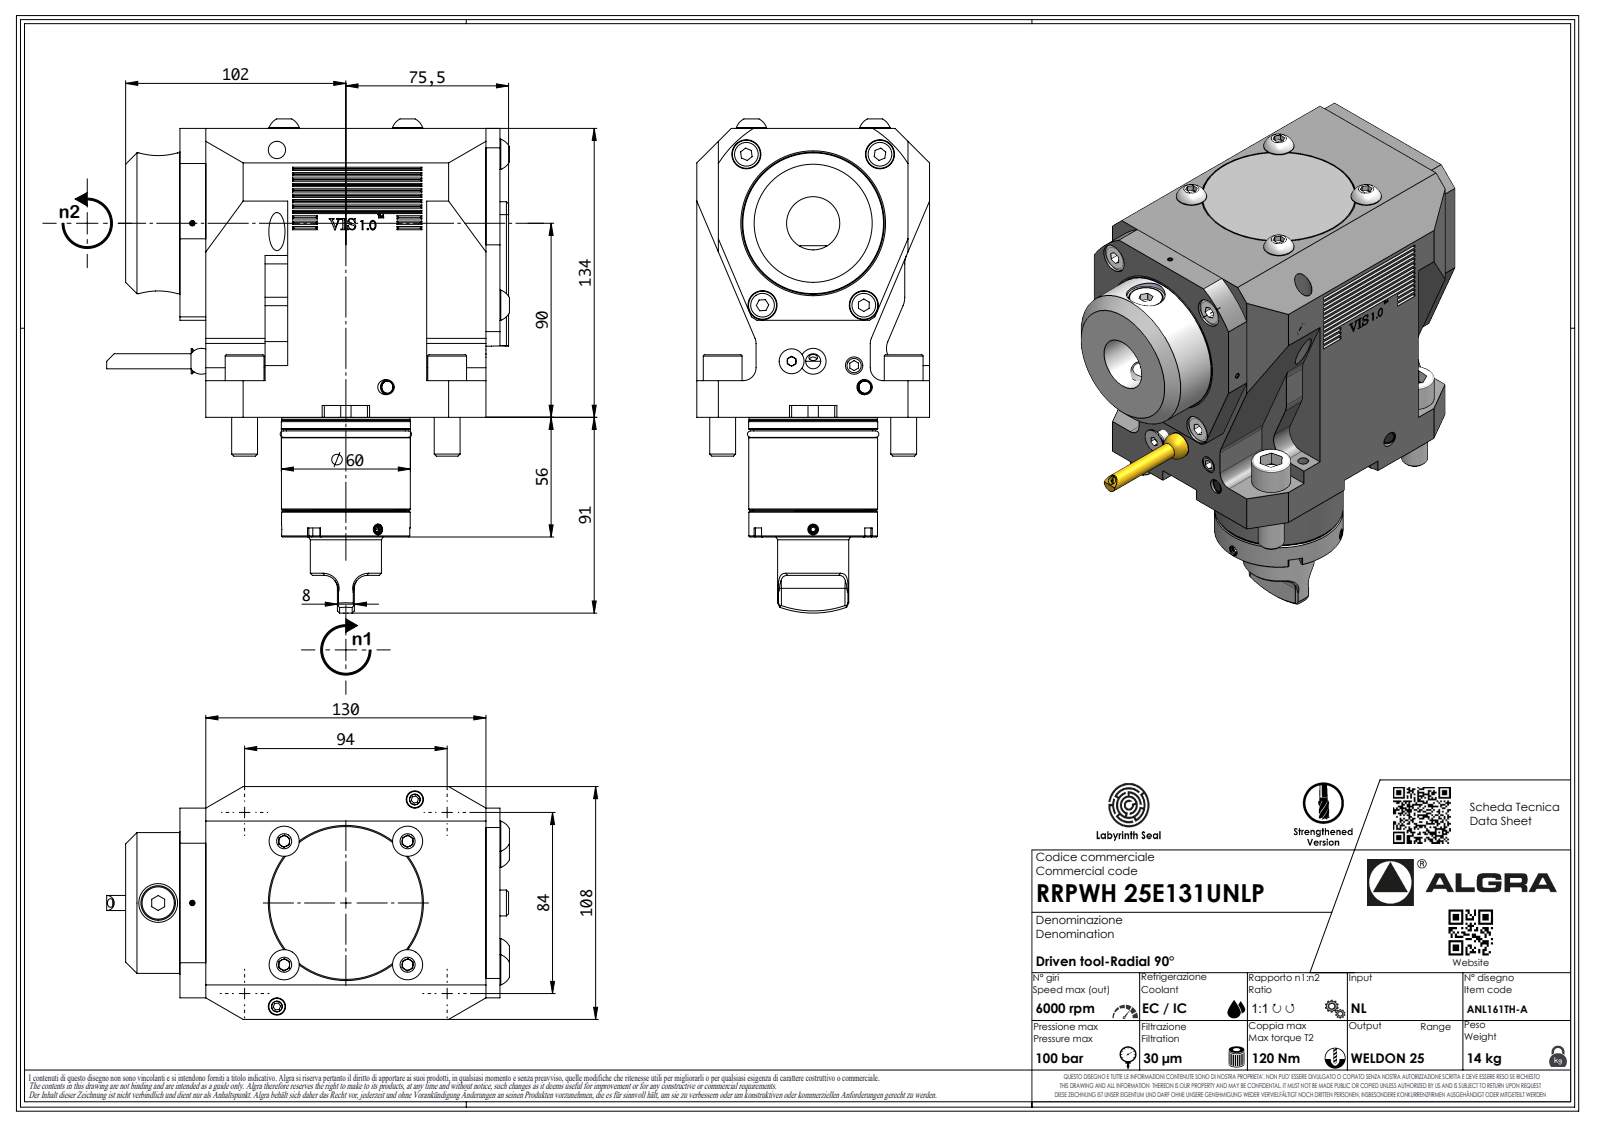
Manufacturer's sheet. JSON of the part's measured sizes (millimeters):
{"part_name": "RRPWH25E131UNLP", "step_written_by": "SolidWorks 2023 (AUTOMOTIVE_DESIGN)", "units": "millimeters", "bodies": {"solids": 1, "faces": 928, "planar": 640, "cylindrical": 111, "other": 177}, "overall_size": [224.8, 177.7, 108], "volume_mm3": 2059000, "surface_area_mm2": 125710, "round_holes": [[2.1, 1]], "round_bosses_or_shafts": [[18, 4], [12, 4], [65.3, 1], [59.9, 1], [59.8, 1], [59.7, 1], [59.5, 1], [55.2, 1]], "partial_cylinders_radius": [[0.2, 21], [8, 18], [6, 11], [0.33, 7], [0.52, 7], [3.7, 7], [10, 4], [3, 3]], "face_to_face_distances": [134, 108, 12, 27.5, 102.5, 148.5, 6.5, 136.5, 38, 5.5]}
